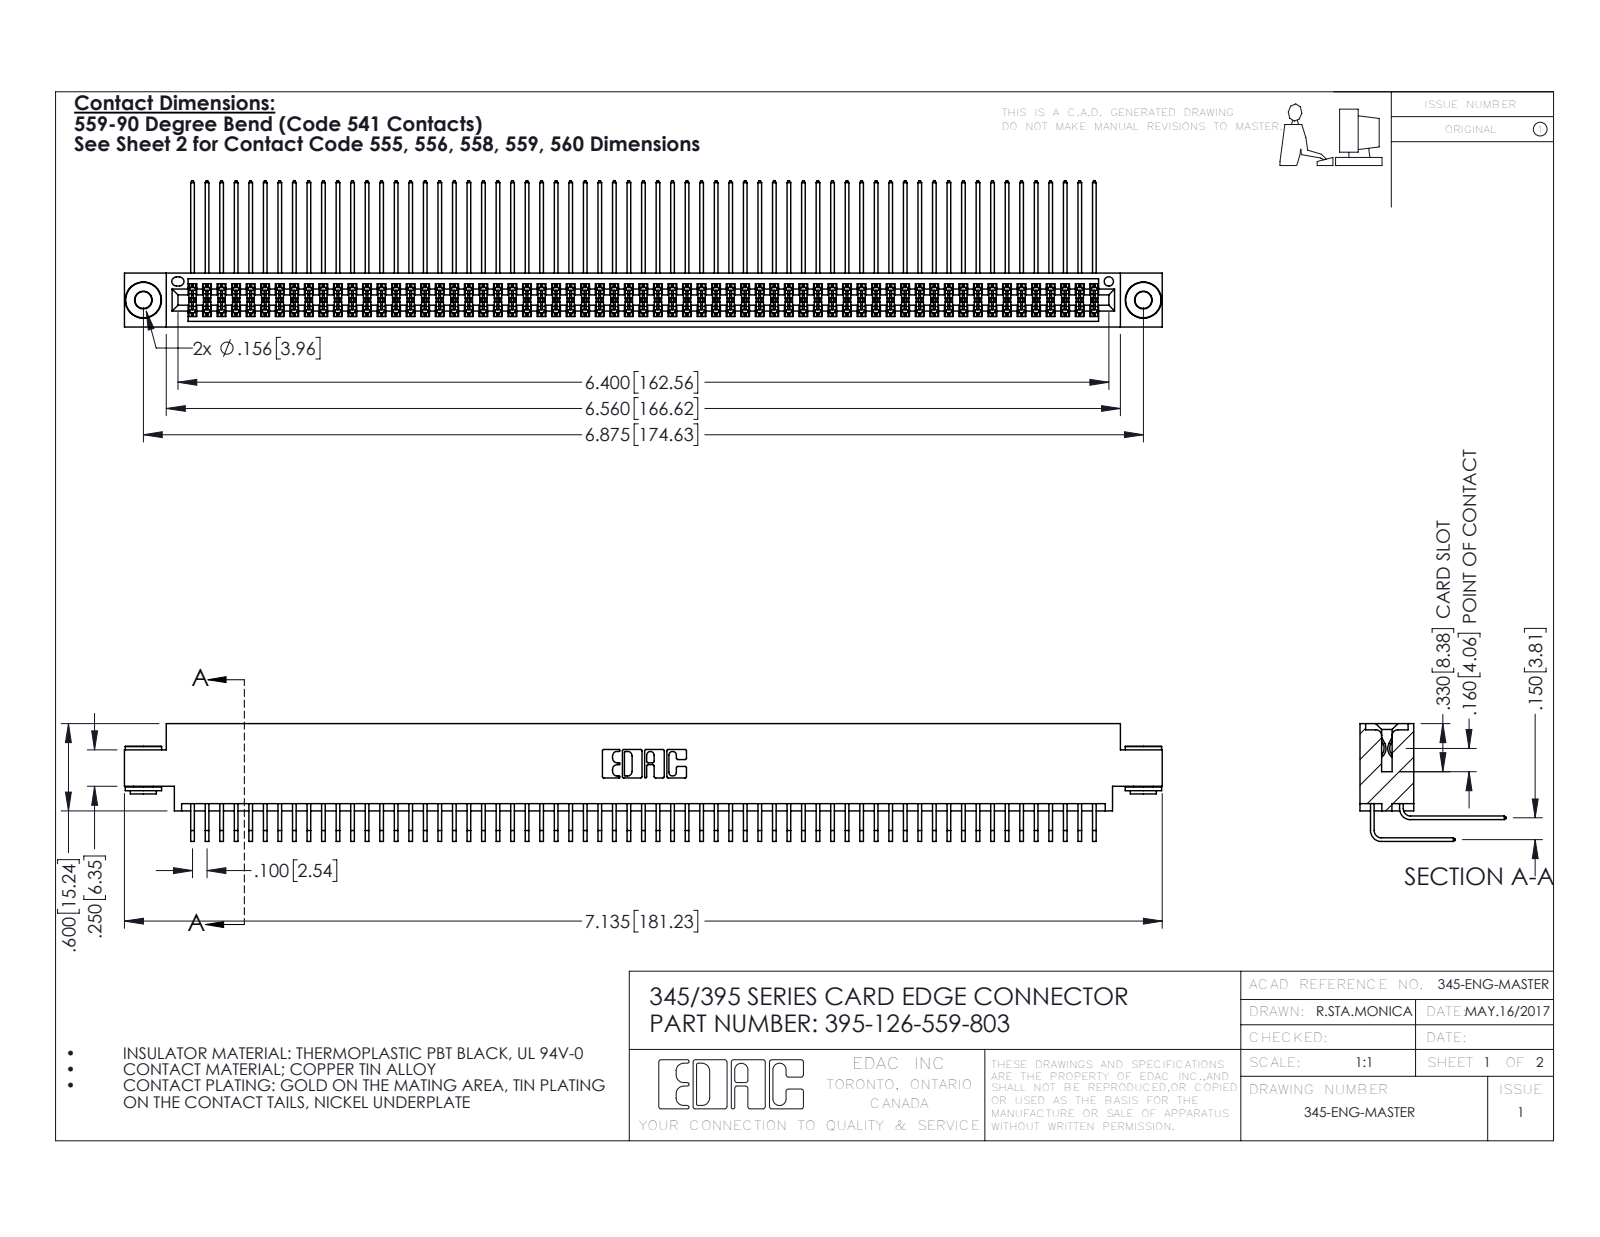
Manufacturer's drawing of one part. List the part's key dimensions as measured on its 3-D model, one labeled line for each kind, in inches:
Part name (STEP PRODUCT): 345 Part_0.170 Offset - 0.156 Dia-TH; 345-292-001_559 Tail - 2; 395-126-559-803; 345-250-002_345-250-002-102 (+1 more)
STEP written by: SolidWorks 2016 (CONFIG_CONTROL_DESIGN)
Units: inches
Bodies: 129 solids, 6720 faces (4504 planar, 2208 cylindrical, 8 other)
Overall size (bounding box): 7.135 × 1.005 × 0.809
Volume: 1.125 in³ · Surface area: 48.7 in²
Round holes (diameter × count): ⌀0.116 ×2, ⌀0.156 ×2, ⌀0.064 ×1
Round bosses / shafts (diameter × count): ⌀0.25 ×2, ⌀0.18 ×2, ⌀0.136 ×2
Partial cylindrical surfaces — rounded edges, fillets, slot ends (radius × count): R0.006 ×189, R0.01 ×22, R0.007 ×6, R0.031 ×6, R0.026 ×3, R0.014 ×2, R0.019 ×2, R0.022 ×2
Main face-to-face distances: 0.072, 0.298, 0.37, 0.2, 0.098, 0.272, 0.025, 0.225, 0.175, 0.15
Hole centre spacings: 0.27, 6.639, 6.875
